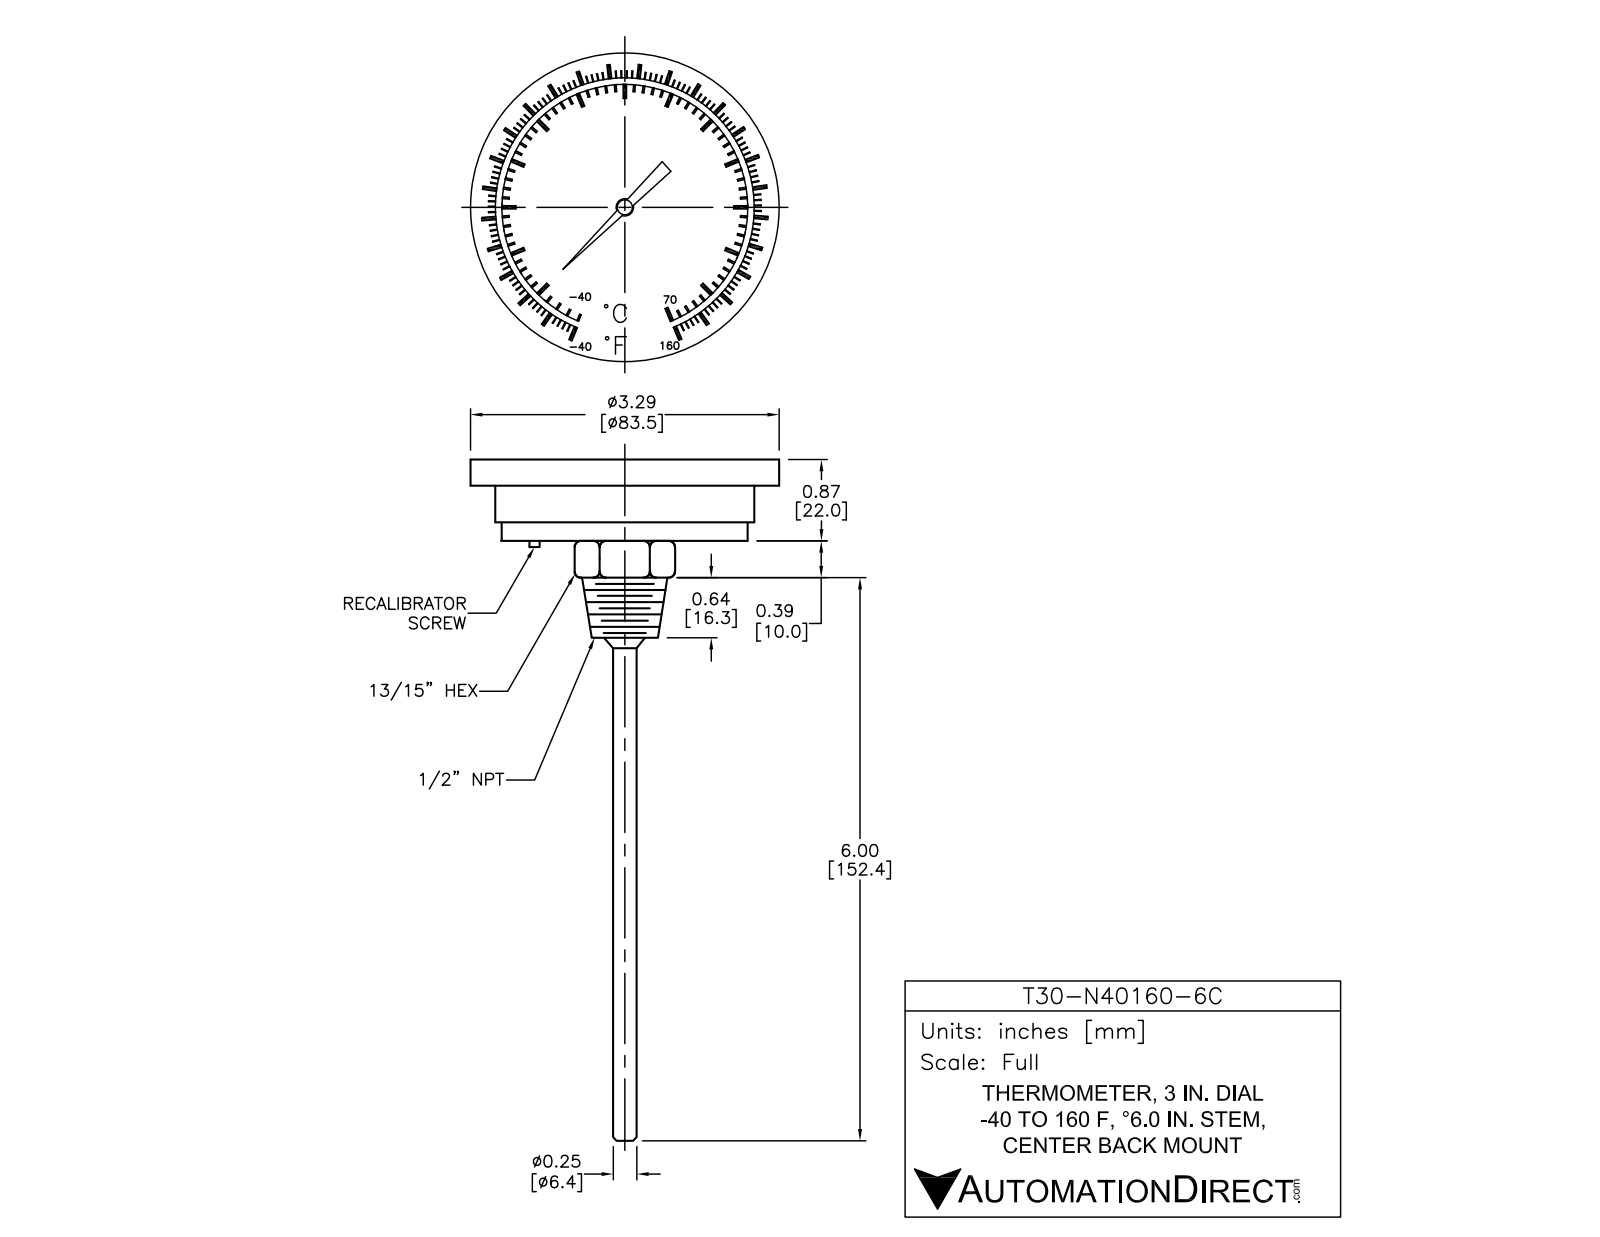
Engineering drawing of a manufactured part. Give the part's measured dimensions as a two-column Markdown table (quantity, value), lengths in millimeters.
| quantity | value |
| --- | --- |
| part name | T30-N40160-6C |
| STEP written by | SolidWorks 2021 (AUTOMOTIVE_DESIGN) |
| units | millimeters |
| bodies | 72 solids, 1258 faces (1113 planar, 85 cylindrical, 60 other) |
| overall size | 184.4 × 83.6 × 83.6 |
| volume | 53 360 mm³ |
| surface area | 23 140 mm² |
| round holes (diameter × count) | 1.7 × 1, 68.3 × 1 |
| round bosses / shafts (diameter × count) | 83.6 × 1, 70.1 × 1, 66.5 × 1, 21.5 × 1, 6.6 × 1 |
| partial cylindrical surfaces (radius × count) | 1 × 1, 18 × 1, 21.8 × 1, 24.6 × 1, 28.4 × 1 |
| main face-to-face distances | 5.6, 2, 7.6, 22.1, 16.5, 14.5, 9.3, 15, 7.4, 7.1 |
